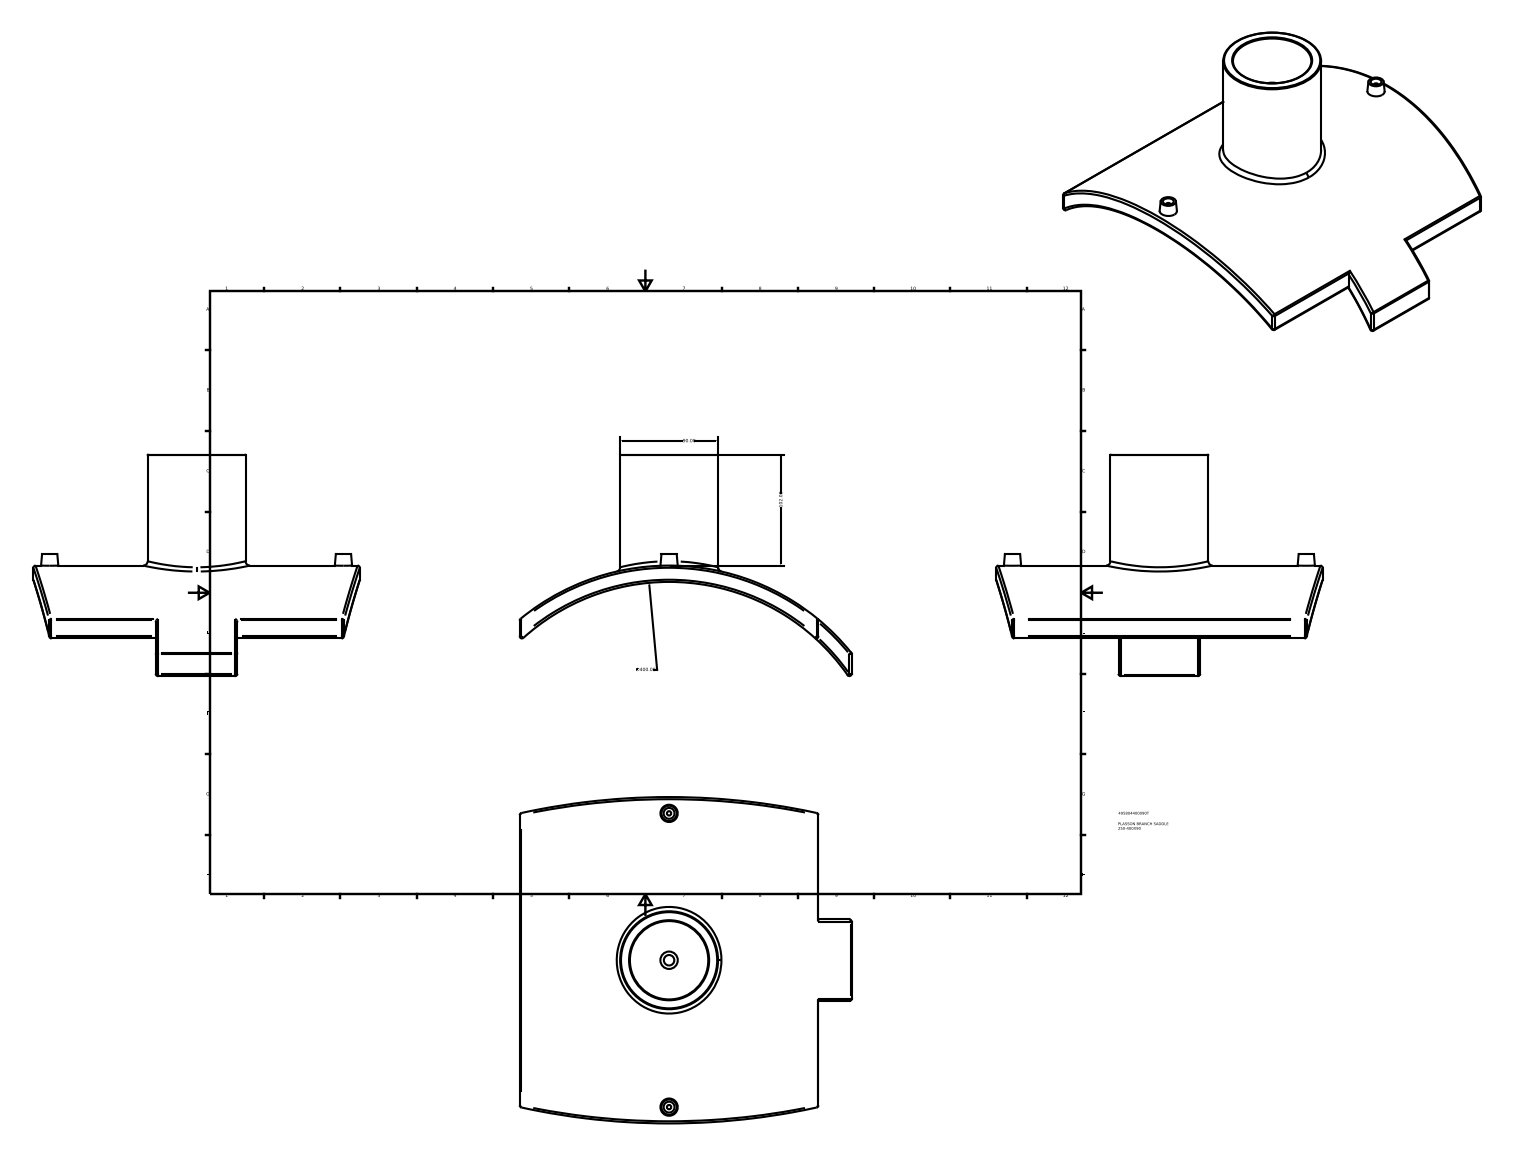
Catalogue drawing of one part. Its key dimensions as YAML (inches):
part_name: "495804400090T"
step_written_by: "Autodesk Inventor 2015 (CONFIG_CONTROL_DESIGN)"
units: inches
bodies: {solids: 1, faces: 66, planar: 14, cylindrical: 27, other: 25}
overall_size: [12.008, 11.811, 8.013]
volume: 97.52
surface_area: 400.8
round_holes:
  - {diameter: 0.394, count: 2}
  - {diameter: 0.378, count: 1}
  - {diameter: 2.835, count: 1}
round_bosses_or_shafts:
  - {diameter: 0.157, count: 2}
  - {diameter: 3.543, count: 1}
  - {diameter: 0.63, count: 1}
partial_cylinders:
  - {radius: 0.079, count: 12}
  - {radius: 25.017, count: 2}
  - {radius: 7.874, count: 1}
  - {radius: 8.465, count: 1}
face_to_face_distances: [10.807, 12.008, 1.201, 2.953, 3.598, 0.551, 4.15, 2.945, 2.394, 1.205]
hole_center_spacings: [5.315, 10.63]
